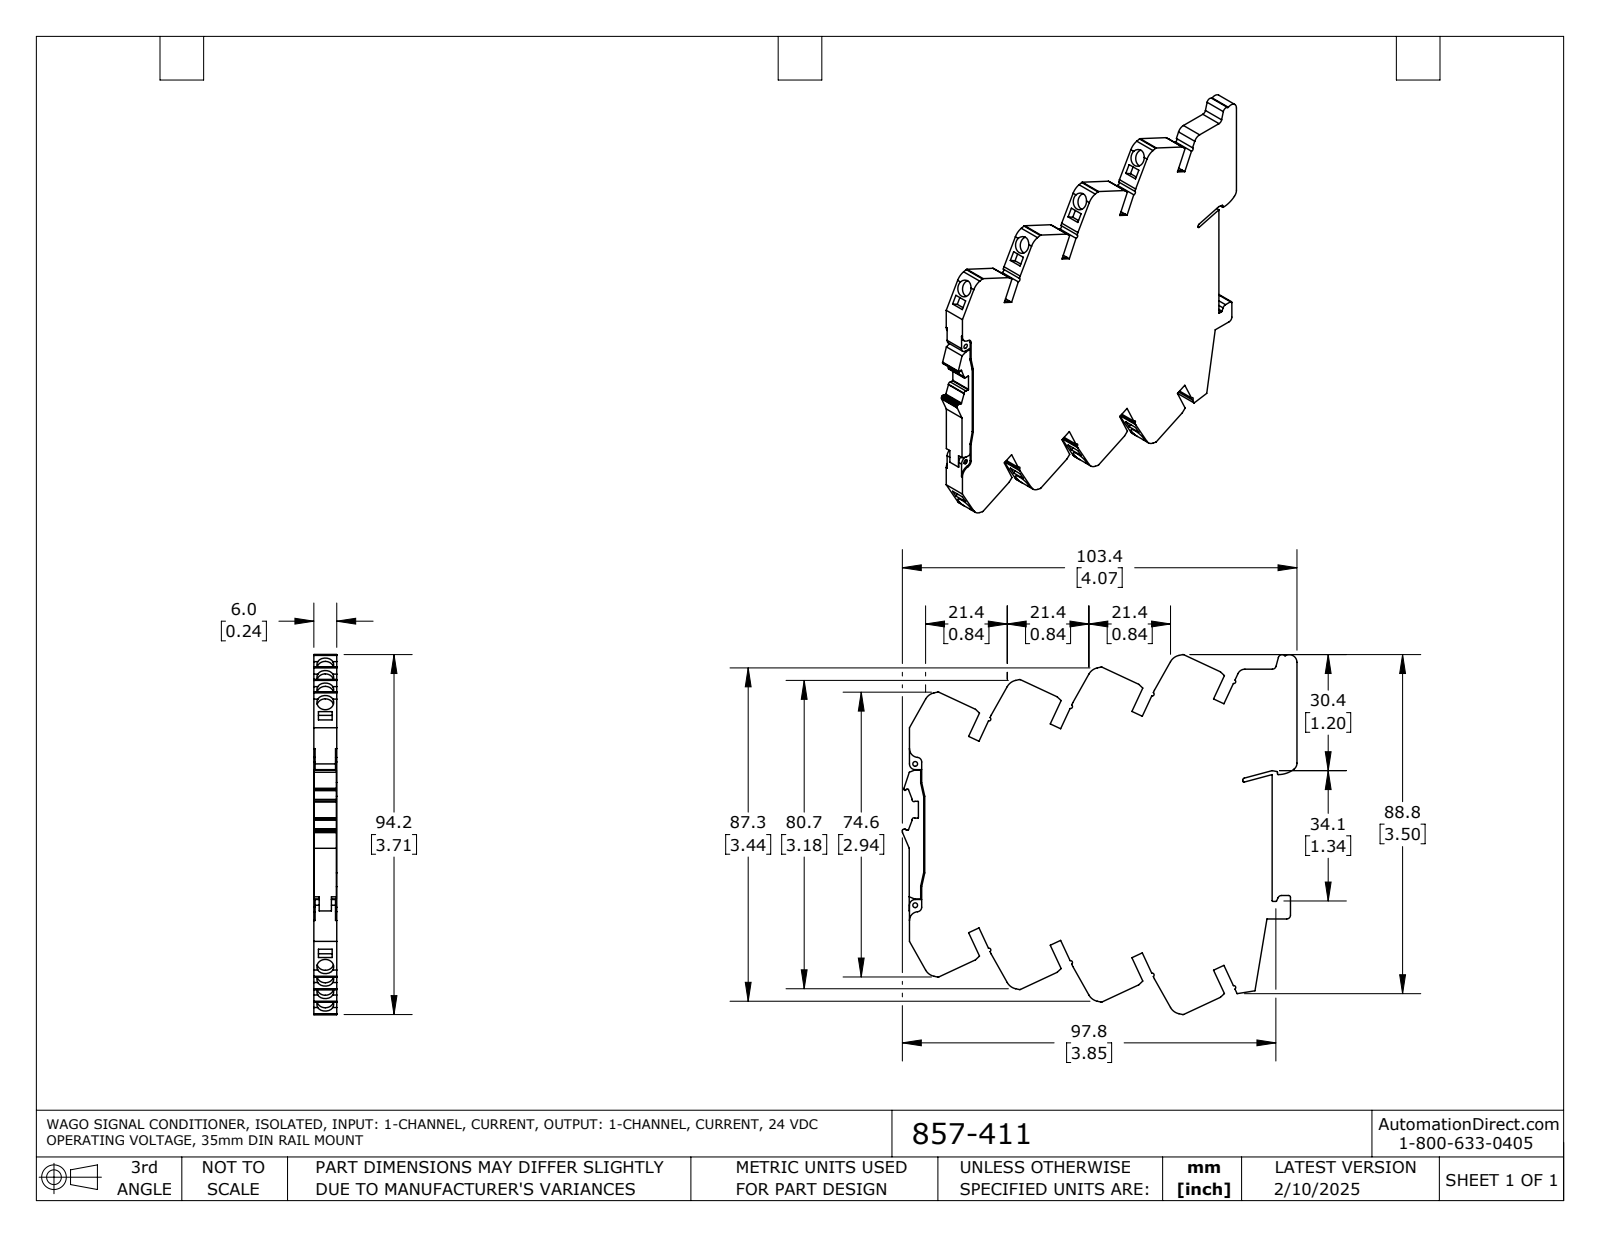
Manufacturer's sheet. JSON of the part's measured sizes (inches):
{"part_name": "857-411", "step_written_by": "SolidWorks 2021 (AUTOMOTIVE_DESIGN)", "units": "inches", "bodies": {"solids": 1, "faces": 317, "planar": 219, "cylindrical": 98, "other": 0}, "overall_size": [4.069, 3.711, 0.236], "volume_in3": 2.681, "surface_area_in2": 29.86, "round_holes": [[0.173, 8], [0.049, 2]], "partial_cylinders_radius": [[0.02, 12], [0.008, 11], [0.016, 8], [0.132, 8], [0.039, 4], [0.012, 3], [0.079, 3], [0.018, 2]], "face_to_face_distances": [0.236, 0.708, 0.67, 0.473, 0.232, 0.472, 0.118, 0.945, 1.417, 0.256], "hole_center_spacings": [0.526, 0.525, 1.051, 1.051, 1.052, 1.457, 1.576, 1.577]}
